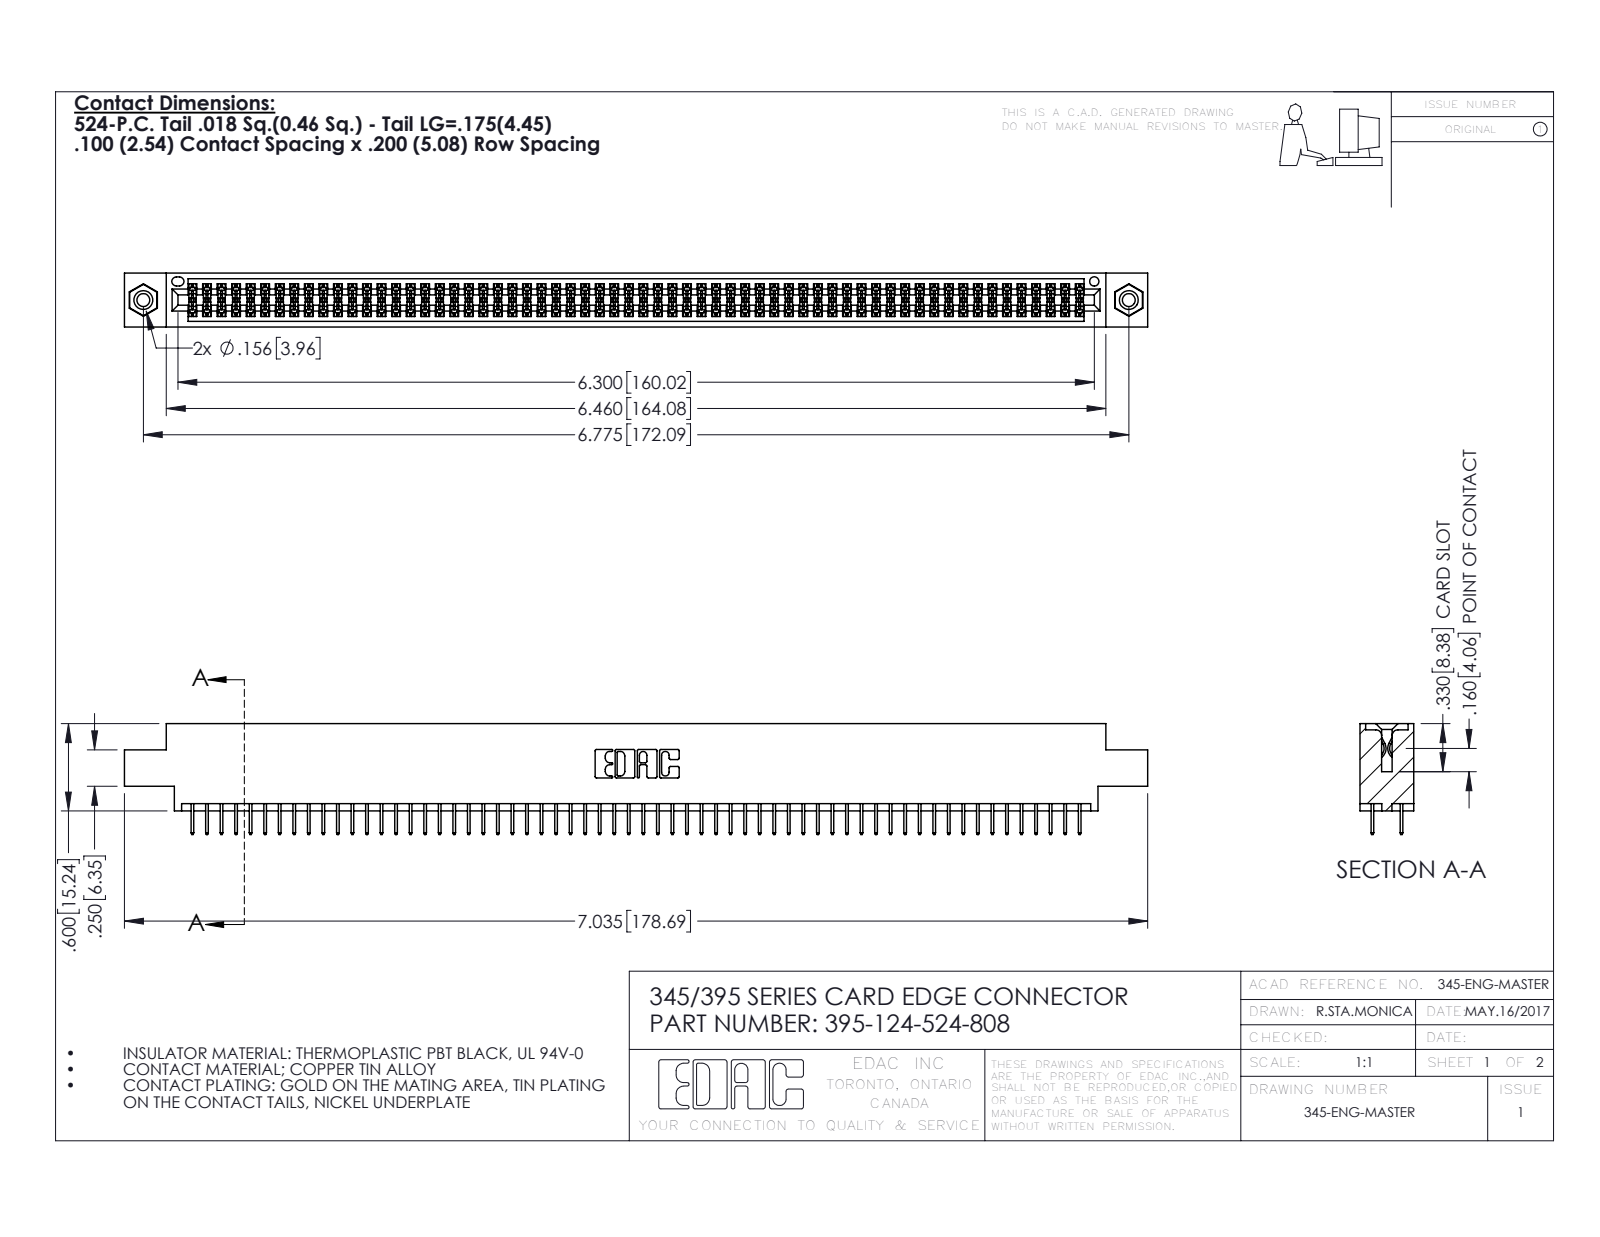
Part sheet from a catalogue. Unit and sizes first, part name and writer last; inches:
Units: inches
Overall size (bounding box): 7.035 × 0.762 × 0.37
Round holes (diameter × count): ⌀0.089 ×2, ⌀0.125 ×2, ⌀0.156 ×2, ⌀0.064 ×1
Round bosses / shafts (diameter × count): ⌀0.155 ×2
Partial cylindrical surfaces — rounded edges, fillets, slot ends (radius × count): R0.006 ×186, R0.01 ×22, R0.007 ×6, R0.031 ×6, R0.026 ×3, R0.014 ×2, R0.019 ×2, R0.022 ×2
Main face-to-face distances: 0.072, 0.298, 0.37, 0.2, 0.098, 0.272, 0.025, 0.225, 0.072, 0.175
Hole centre spacings: 0.27, 6.539, 6.775
Volume: 1.052 in³ · Surface area: 39.57 in²
Bodies: 127 solids, 6886 faces (4952 planar, 1918 cylindrical, 16 other)
Part name (STEP PRODUCT): 345-250-001_345-250-003-102; 345-292-001_345-293-124; 345 Part_0.170 Offset - 0.156 Dia-TI; 395-124-524-808
STEP written by: SolidWorks 2016 (CONFIG_CONTROL_DESIGN)
